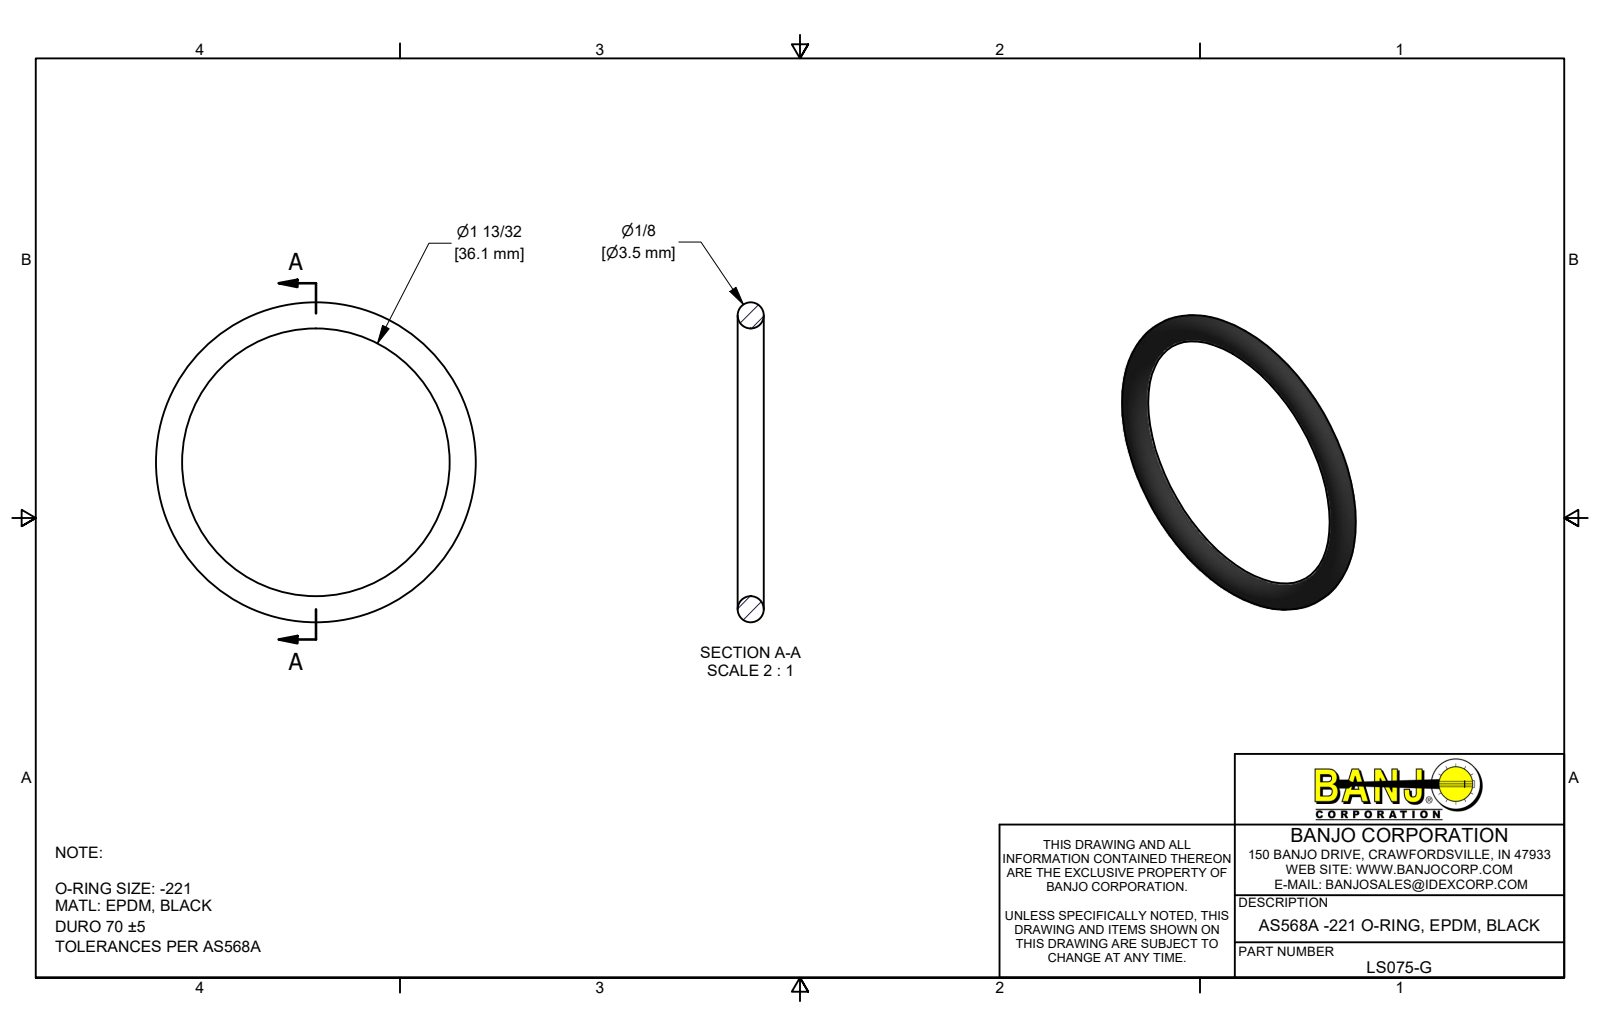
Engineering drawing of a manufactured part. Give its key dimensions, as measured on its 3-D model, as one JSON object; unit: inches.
{"part_name": "LS075-G", "step_written_by": "Autodesk Inventor 2019 (AUTOMOTIVE_DESIGN)", "units": "inches", "bodies": {"solids": 1, "faces": 1, "planar": 0, "cylindrical": 0, "other": 1}, "overall_size": [1.699, 1.699, 0.139], "volume_in3": 0.074, "surface_area_in2": 2.14}
